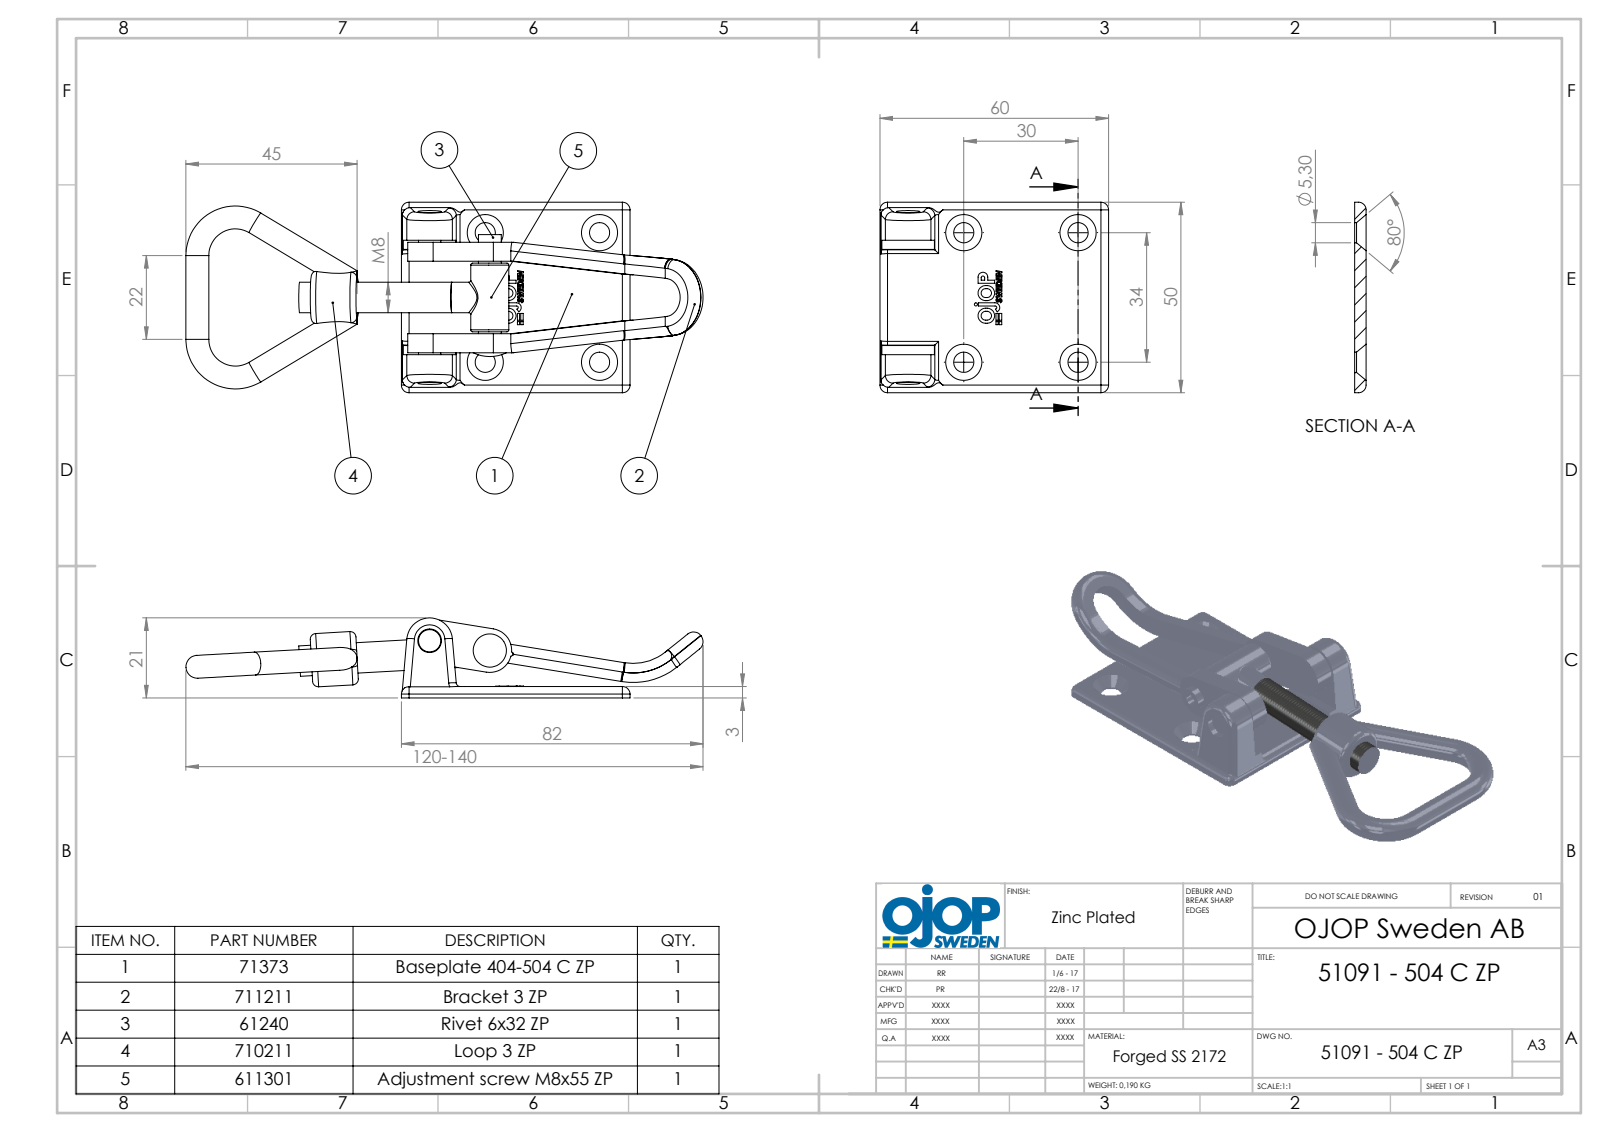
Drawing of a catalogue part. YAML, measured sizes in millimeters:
part_name: "Hålnit 6x32; Ring 3; Justerskruv M8; 51091 - 504 C FZB (+2 more)"
step_written_by: "SolidWorks 2015 (AUTOMOTIVE_DESIGN)"
units: millimeters
bodies: {solids: 5, faces: 204, planar: 56, cylindrical: 83, other: 65}
overall_size: [133.3, 50, 21.15]
volume: 25590
surface_area: 18031
round_holes:
  - {diameter: 5.3, count: 4}
  - {diameter: 6.2, count: 2}
  - {diameter: 3, count: 1}
  - {diameter: 6.3, count: 1}
  - {diameter: 8.1, count: 1}
round_bosses_or_shafts:
  - {diameter: 6, count: 4}
  - {diameter: 10, count: 1}
  - {diameter: 8.01, count: 1}
  - {diameter: 8, count: 1}
  - {diameter: 5.85, count: 1}
partial_cylinders:
  - {radius: 2, count: 8}
  - {radius: 2.5, count: 8}
  - {radius: 1, count: 4}
  - {radius: 6.99, count: 4}
  - {radius: 1.5, count: 2}
  - {radius: 6.15, count: 2}
  - {radius: 2.4, count: 1}
  - {radius: 5, count: 1}
face_to_face_distances: [3, 5, 25, 30, 20, 3.67, 8.67, 10, 15, 35]
hole_center_spacings: [30, 34, 45.34, 16]
